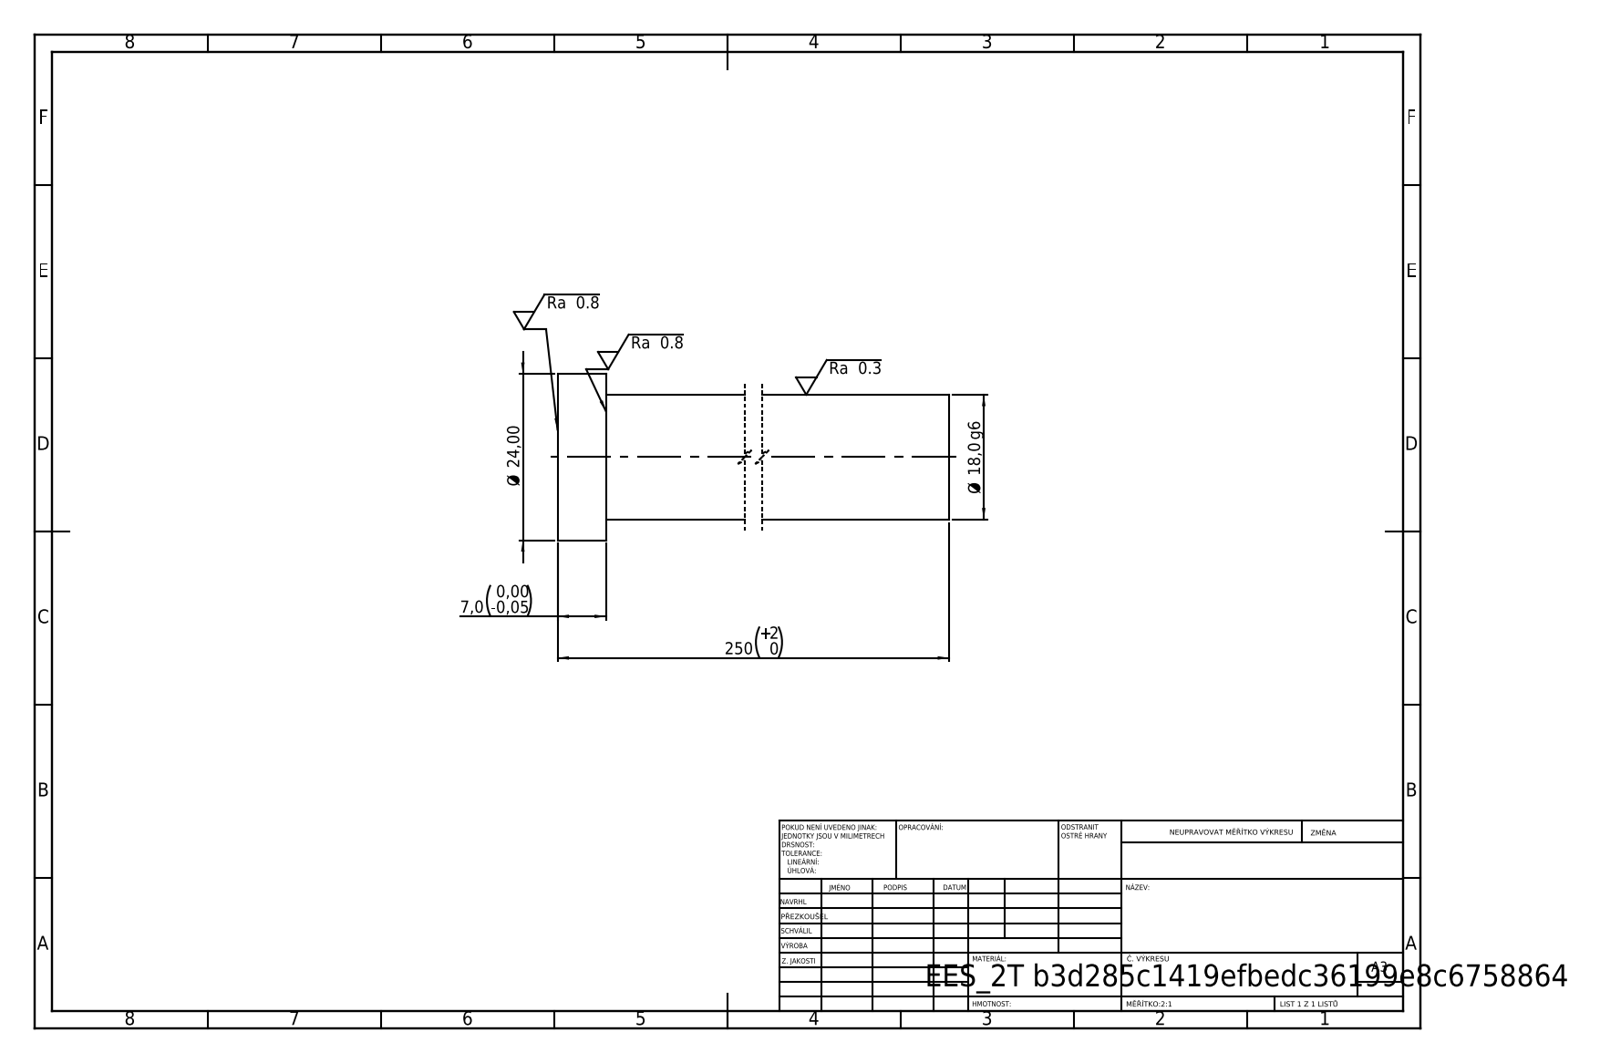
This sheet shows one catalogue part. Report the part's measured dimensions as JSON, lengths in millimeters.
{"step_written_by": "SolidWorks 2019 (CONFIG_CONTROL_DESIGN)", "units": "millimeters", "bodies": {"solids": 1, "faces": 7, "planar": 3, "cylindrical": 4, "other": 0}, "overall_size": [250, 24, 24], "volume_mm3": 65003, "surface_area_mm2": 15174, "round_bosses_or_shafts": [[24, 1], [18, 1]], "face_to_face_distances": [250, 7, 243]}
